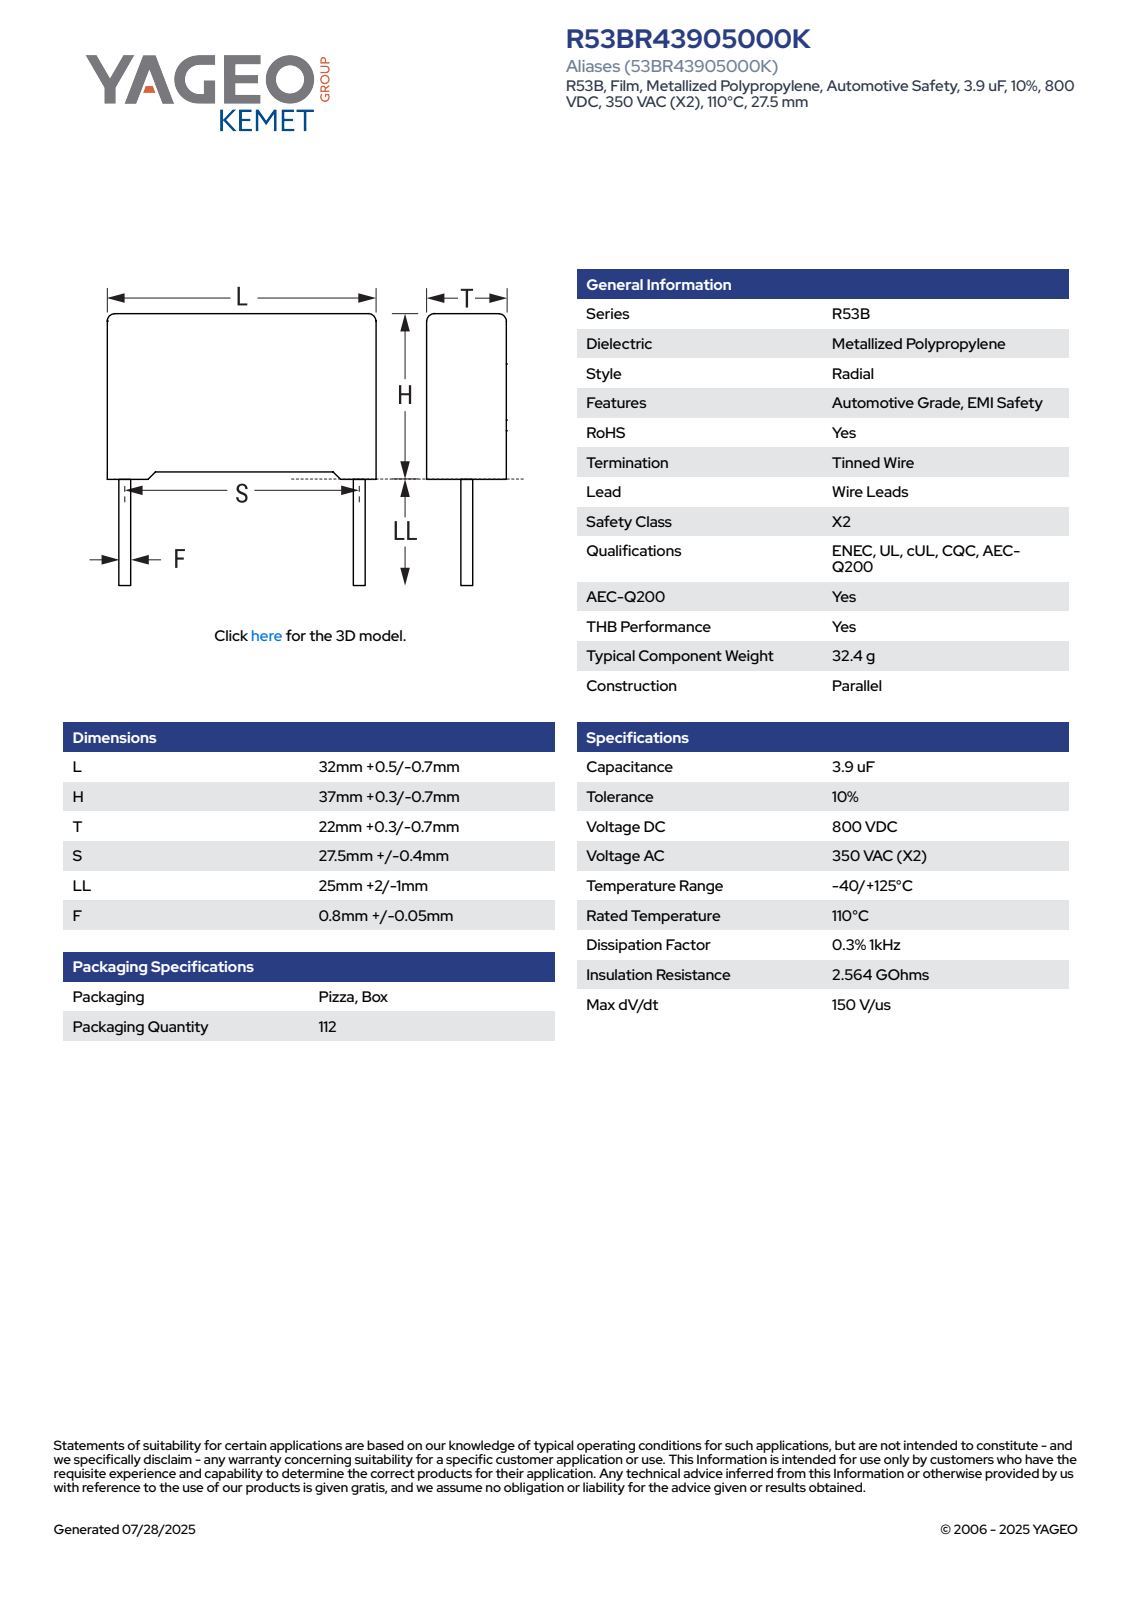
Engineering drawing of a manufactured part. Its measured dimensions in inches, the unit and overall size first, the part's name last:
Units: inches
Overall size (bounding box): 2.531 × 1.28 × 0.878
Round bosses / shafts (diameter × count): ⌀0.033 ×2
Partial cylindrical surfaces — rounded edges, fillets, slot ends (radius × count): R0.02 ×4
Main face-to-face distances: 0.878, 1.28, 1.418, 0.021, 1.439, 0.03, 0.051, 1.469, 0.043, 1.237
Volume: 1.604 in³ · Surface area: 8.888 in²
Bodies: 4 solids, 85 faces (77 planar, 8 cylindrical, 0 other)
Part name (STEP PRODUCT): CFR_RB2_32X37X22_L32.5H37.3T22.3S27.5LL27F0.85
STEP written by: SolidWorks 2021 (AUTOMOTIVE_DESIGN)
